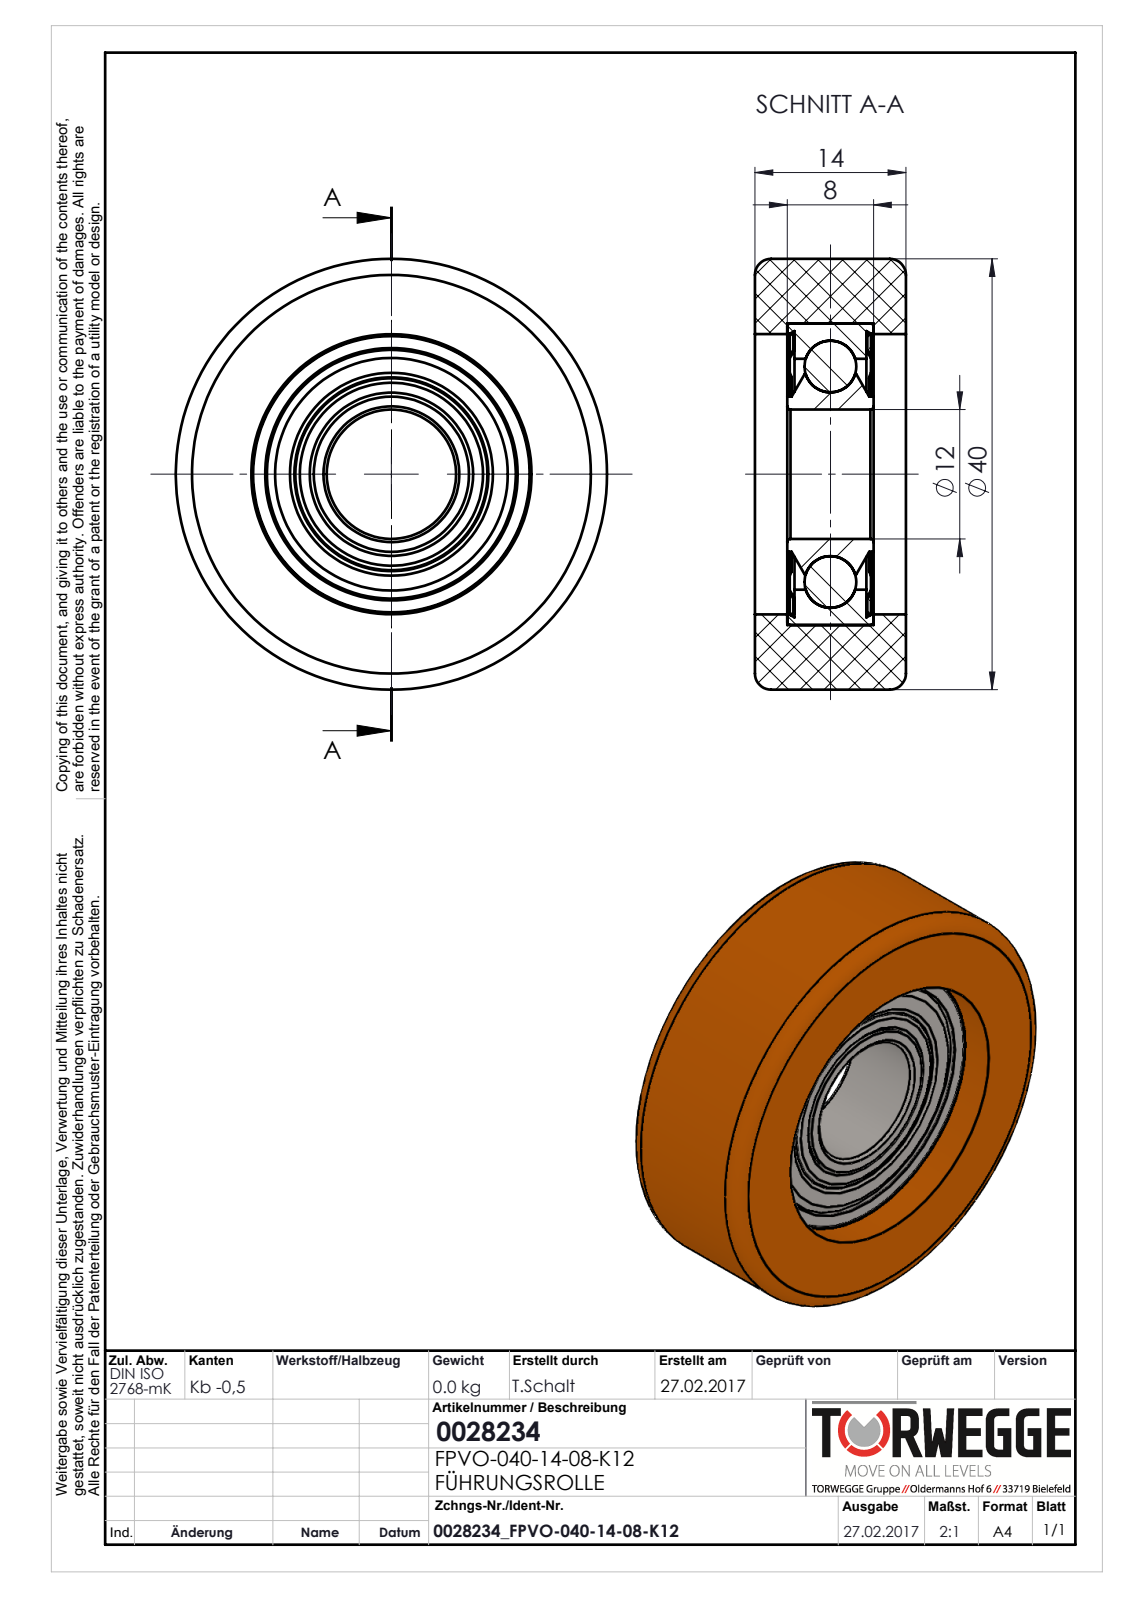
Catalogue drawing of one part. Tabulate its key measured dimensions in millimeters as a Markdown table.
| quantity | value |
| --- | --- |
| part name | 0028234_FPVO-040-14-08-K12; snr_6001zz_2_04; snr_6001zz_2_01; snr_6001zz_2 (+4 more) |
| STEP written by | SolidWorks 2016 (CONFIG_CONTROL_DESIGN) |
| units | millimeters |
| bodies | 6 solids, 90 faces (30 planar, 16 cylindrical, 44 other) |
| overall size | 40 × 40 × 14 |
| volume | 12 049 mm³ |
| surface area | 9 948 mm² |
| round holes (diameter × count) | 12 × 1, 15.15 × 1, 21.44 × 1, 23.42 × 1, 26 × 1, 28 × 1 |
| round bosses / shafts (diameter × count) | 40 × 1, 18.56 × 1, 14.4 × 1 |
| main face-to-face distances | 7.2, 0.44, 3.67, 10.33, 14, 3.13, 10.87, 0.54, 3.23, 10.77 |
